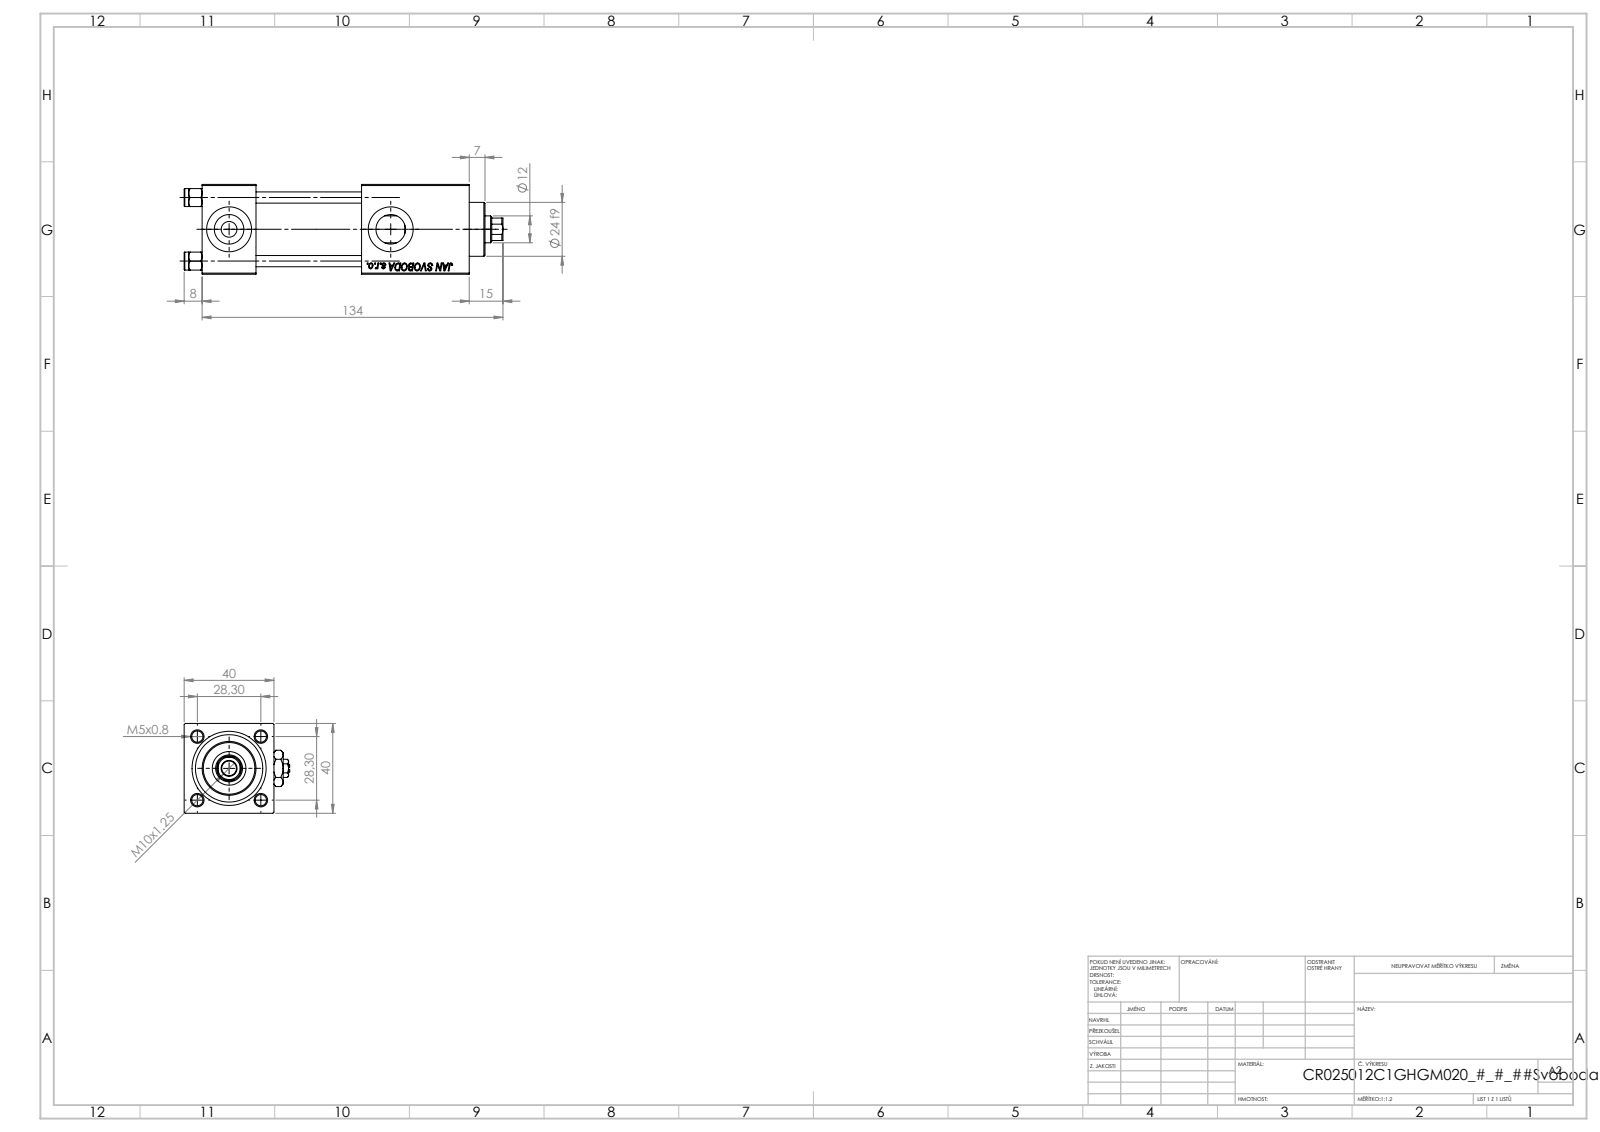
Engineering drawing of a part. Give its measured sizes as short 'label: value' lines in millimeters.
name: V215CR_C_TYCINKA; V215CR_VCP_C; Zatka_pro_OIL_PORT; V215CR_C_Body (+2 more)
written by: SolidWorks 2019 (CONFIG_CONTROL_DESIGN)
unit: mm
bodies: 12 solids, 1195 faces (549 planar, 90 cylindrical, 556 other)
size: 142 × 47 × 40
volume: 141 739 mm³; area: 55 185 mm²
holes: 4× ⌀5, 3× ⌀20, 2× ⌀7, 2× ⌀13.16, 1× ⌀6.5, 1× ⌀12, 1× ⌀15, 1× ⌀25, 1× ⌀30
bosses: 4× ⌀8, 1× ⌀31, 1× ⌀24
rounds: 1× R5.5
face distances: 40, 24, 90.3, 66.3, 48, 47, 71, 19.3, 119, 95
hole spacings: 20.01, 28.3, 40.02, 72
